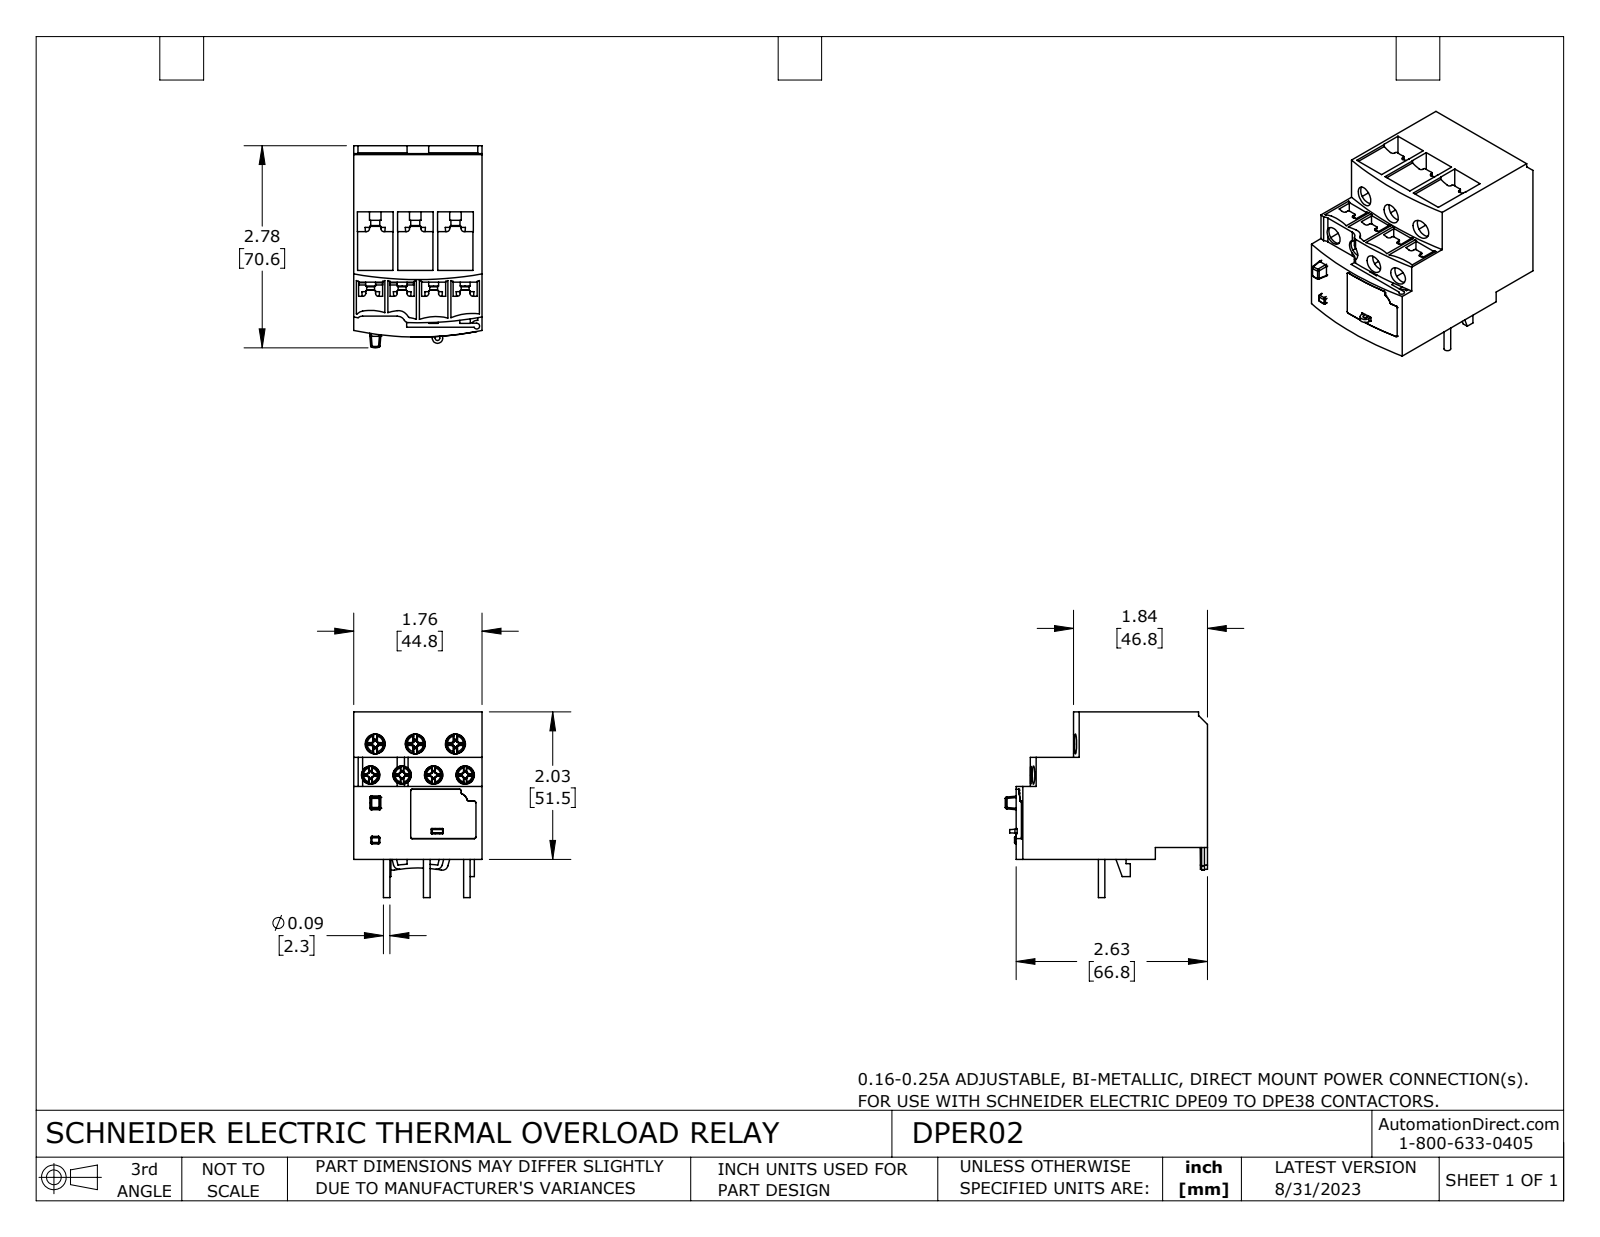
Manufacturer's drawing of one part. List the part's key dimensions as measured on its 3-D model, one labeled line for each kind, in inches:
Part name (STEP PRODUCT): DPER02
STEP written by: SolidWorks 2021 (CONFIG_CONTROL_DESIGN)
Units: inches
Bodies: 16 solids, 1212 faces (676 planar, 269 cylindrical, 267 other)
Overall size (bounding box): 2.778 × 2.553 × 1.764
Volume: 6.953 in³ · Surface area: 47.15 in²
Round holes (diameter × count): ⌀0.252 ×4, ⌀0.276 ×3, ⌀0.079 ×2, ⌀0.118 ×2, ⌀0.059 ×1, ⌀0.244 ×1
Round bosses / shafts (diameter × count): ⌀0.091 ×12, ⌀0.138 ×4, ⌀0.108 ×4, ⌀0.157 ×3, ⌀0.154 ×3, ⌀0.124 ×3, ⌀0.118 ×1, ⌀0.107 ×1
Partial cylindrical surfaces — rounded edges, fillets, slot ends (radius × count): R0.02 ×52, R0.039 ×22, R0.004 ×19, R0.012 ×8, R0.008 ×6, R0.63 ×6, R0.079 ×4, R0.024 ×2
Main face-to-face distances: 1.764, 0.165, 2.028, 1.863, 0.909, 0.551, 0.618, 1.409, 1.245, 2.497
Hole centre spacings: 0.433, 0.551, 0.866, 0.334, 0.381, 0.404, 0.422, 0.449
